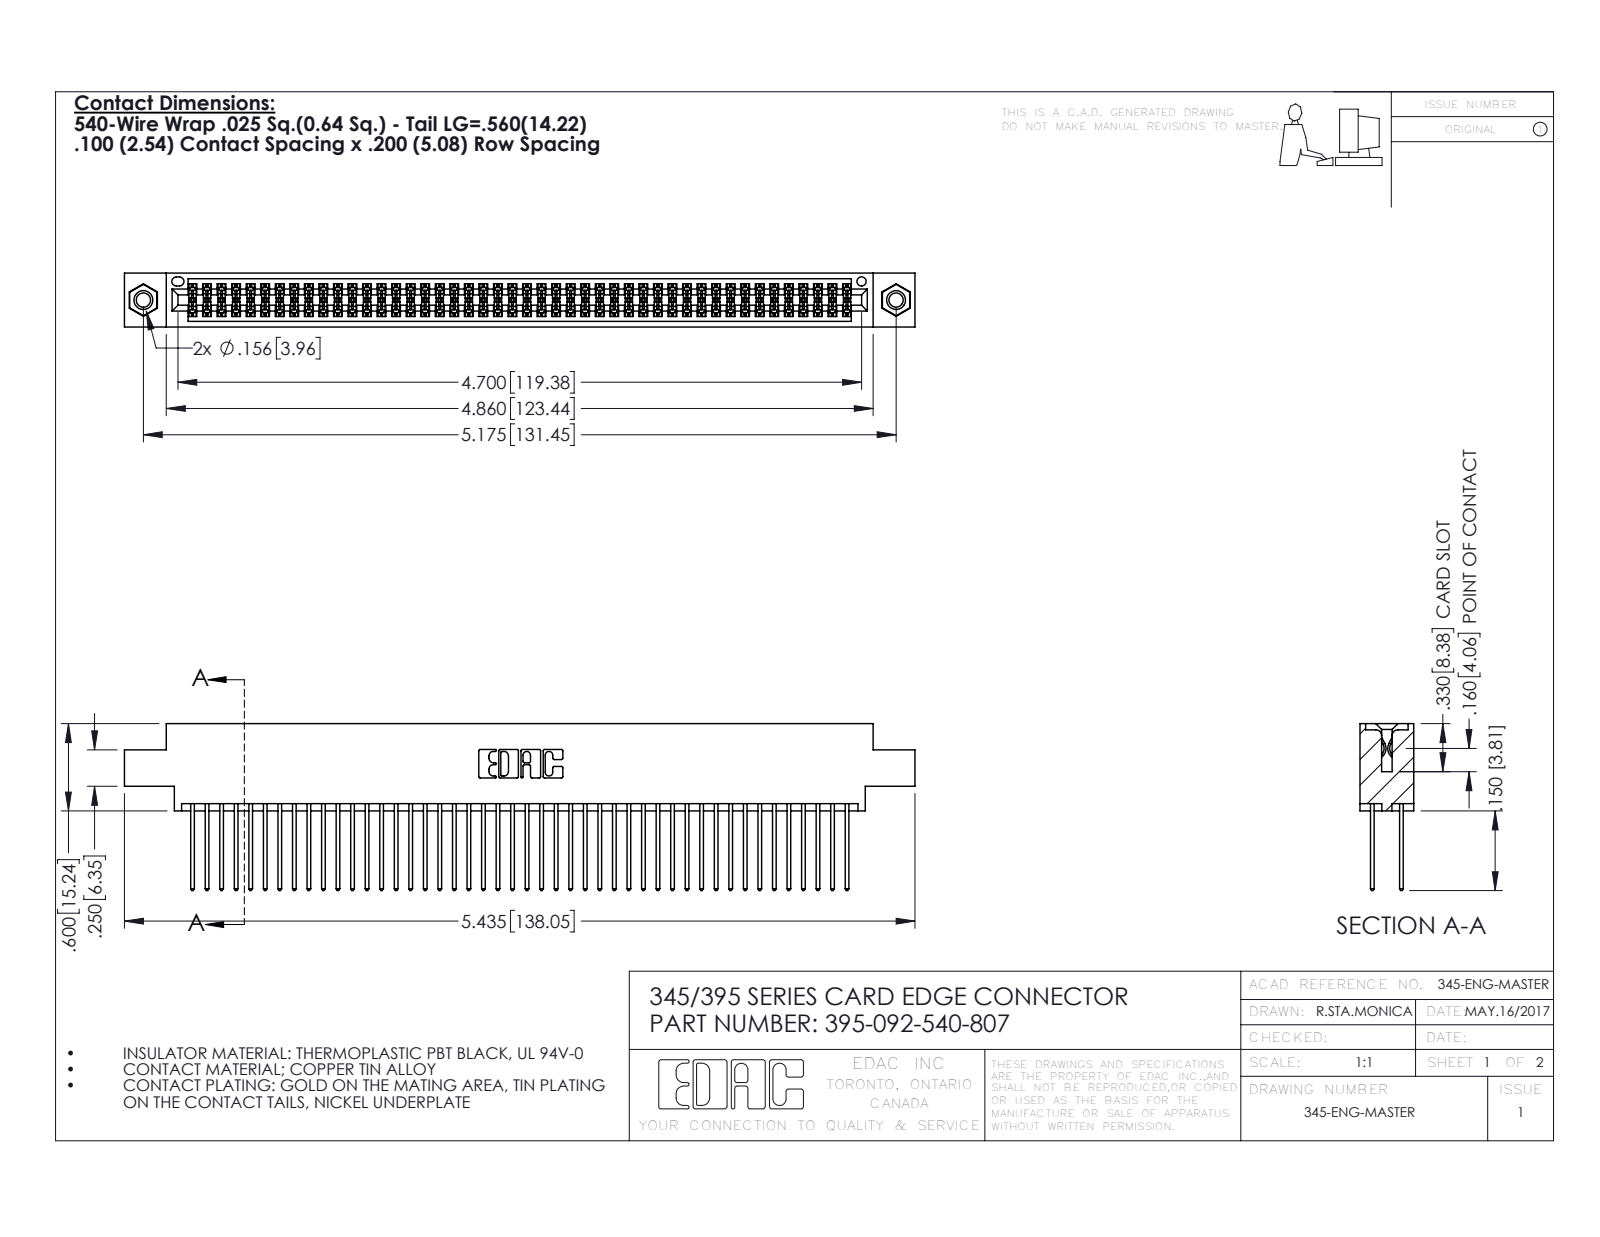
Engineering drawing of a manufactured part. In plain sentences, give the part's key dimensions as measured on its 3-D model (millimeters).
The part is named "345-292-001_345-293-140; 345-250-001_345-250-005-103; 395-092-540-807; 345 Part_0.170 Offset - 0.156 Dia-TI". Its 3-D file was written by "SolidWorks 2016 (CONFIG_CONTROL_DESIGN)". It is 95 solids with 4790 faces: 3152 planar, 1622 cylindrical and 16 other. Overall it measures 138 by 29.1 by 9.4 millimeters. Its volume is 13 700 cubic millimeters and its surface area 22 070 square millimeters. Round holes: 2 of diameter 2.5, 2 of diameter 3.2, 2 of diameter 4, 1 of diameter 1.6. Round bosses or shafts: 2 of diameter 3.9. Partial cylindrical surfaces (rounded edges, fillets, slot ends): 138 of radius 0.2, 92 of radius 0.3, 22 of radius 0.3, 6 of radius 0.2, 6 of radius 0.8, 3 of radius 0.7, 2 of radius 0.4, 2 of radius 0.5. The main face-to-face distances are 1.8, 7.6, 5.1, 2.5, 6.9, 0.6, 9.4, 5.7, 4.4, 3.8. The hole center spacings are 6.9, 125.5, 131.4.
